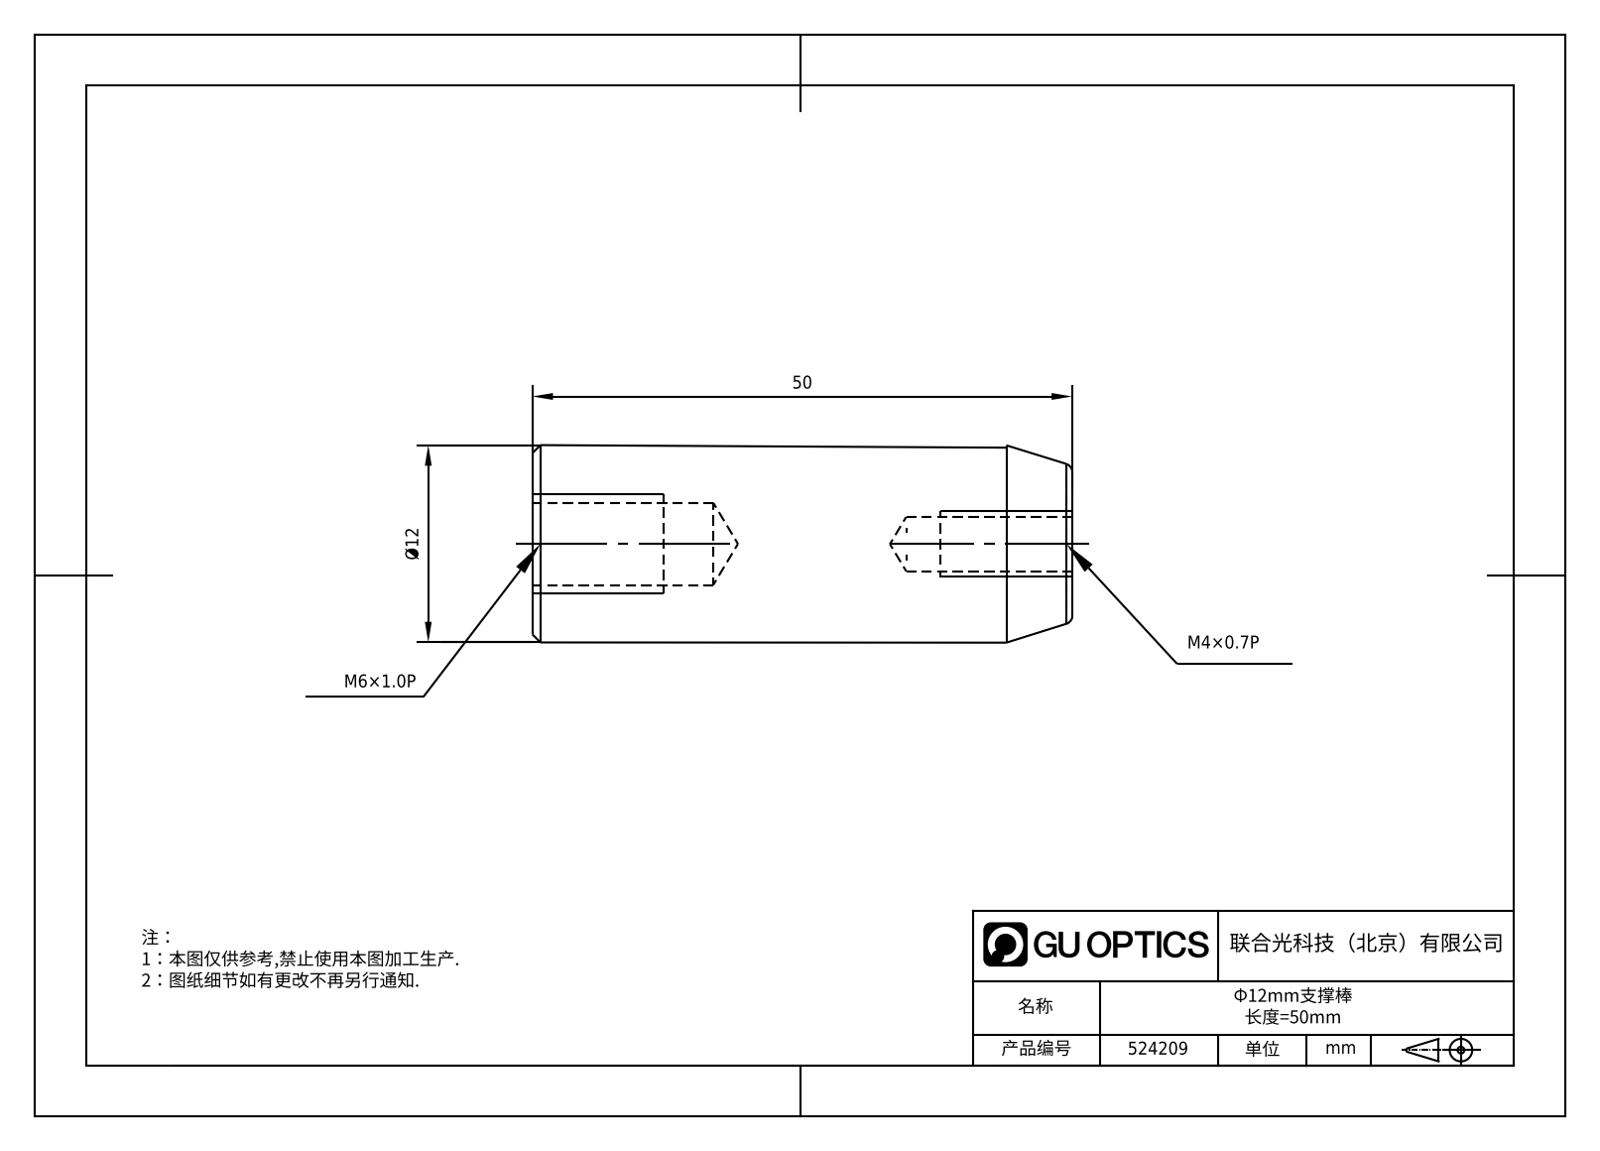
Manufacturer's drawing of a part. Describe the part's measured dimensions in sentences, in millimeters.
The part is named "524209". Its 3-D file was written by "SolidWorks 2020 (CONFIG_CONTROL_DESIGN)". It is 1 solid with 10 faces: 2 planar, 3 cylindrical and 5 other. Overall it measures 50 by 12 by 12 millimeters. Its volume is 5 247 cubic millimeters and its surface area 2 327 square millimeters. Round holes: 1 of diameter 3.3, 1 of diameter 5. Round bosses or shafts: 1 of diameter 12. The main face-to-face distances are 50.
